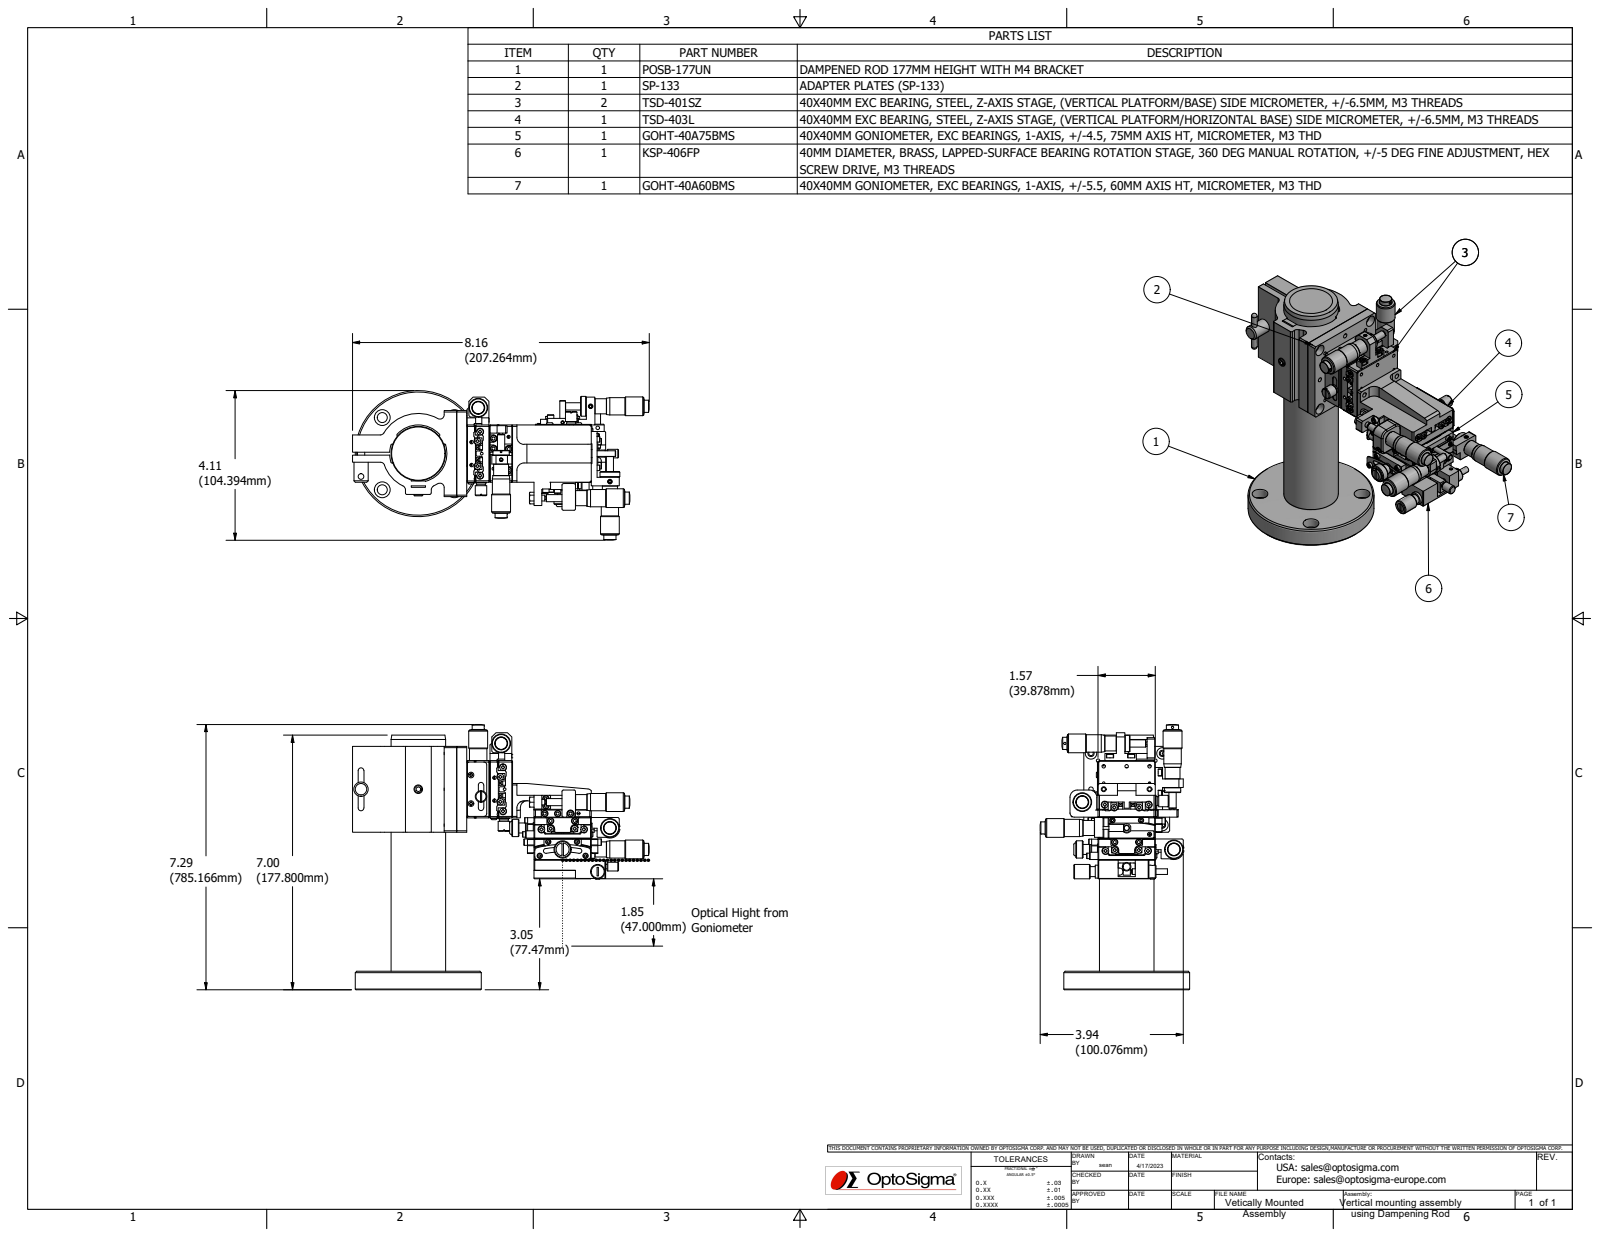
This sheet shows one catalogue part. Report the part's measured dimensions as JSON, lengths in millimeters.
{"part_name": "Vertical Mounter 6 axis assembly; POSB-177UN; SP-133; TSD-401SZ (+4 more)", "step_written_by": "Autodesk Inventor 2022 (AUTOMOTIVE_DESIGN)", "units": "millimeters", "bodies": {"solids": 46, "faces": 4650, "planar": 2590, "cylindrical": 1471, "other": 589}, "overall_size": [207.3, 185.25, 104.5], "volume_mm3": 532008, "surface_area_mm2": 212485, "round_holes": [[1.8, 65], [2.46, 40], [1.57, 31], [2.11, 31], [1.57, 30], [3.24, 21], [2.4, 20], [3, 19], [2, 18], [1.6, 16], [6, 12], [2.6, 10]], "round_bosses_or_shafts": [[4.5, 47], [3, 32], [2, 22], [4, 15], [2.5, 12], [5, 11], [2.6, 9], [2.4, 9]], "partial_cylinders_radius": [[0.8, 101], [1, 47], [2.5, 29], [3, 22], [2, 20], [0.5, 11], [0.78, 7], [0.1, 6]], "face_to_face_distances": [7, 16, 15, 10, 19, 13, 0.5, 77.5, 50, 40], "hole_center_spacings": [25, 7, 31.62, 47.87, 14.14, 18.03, 18.36, 20.62]}
